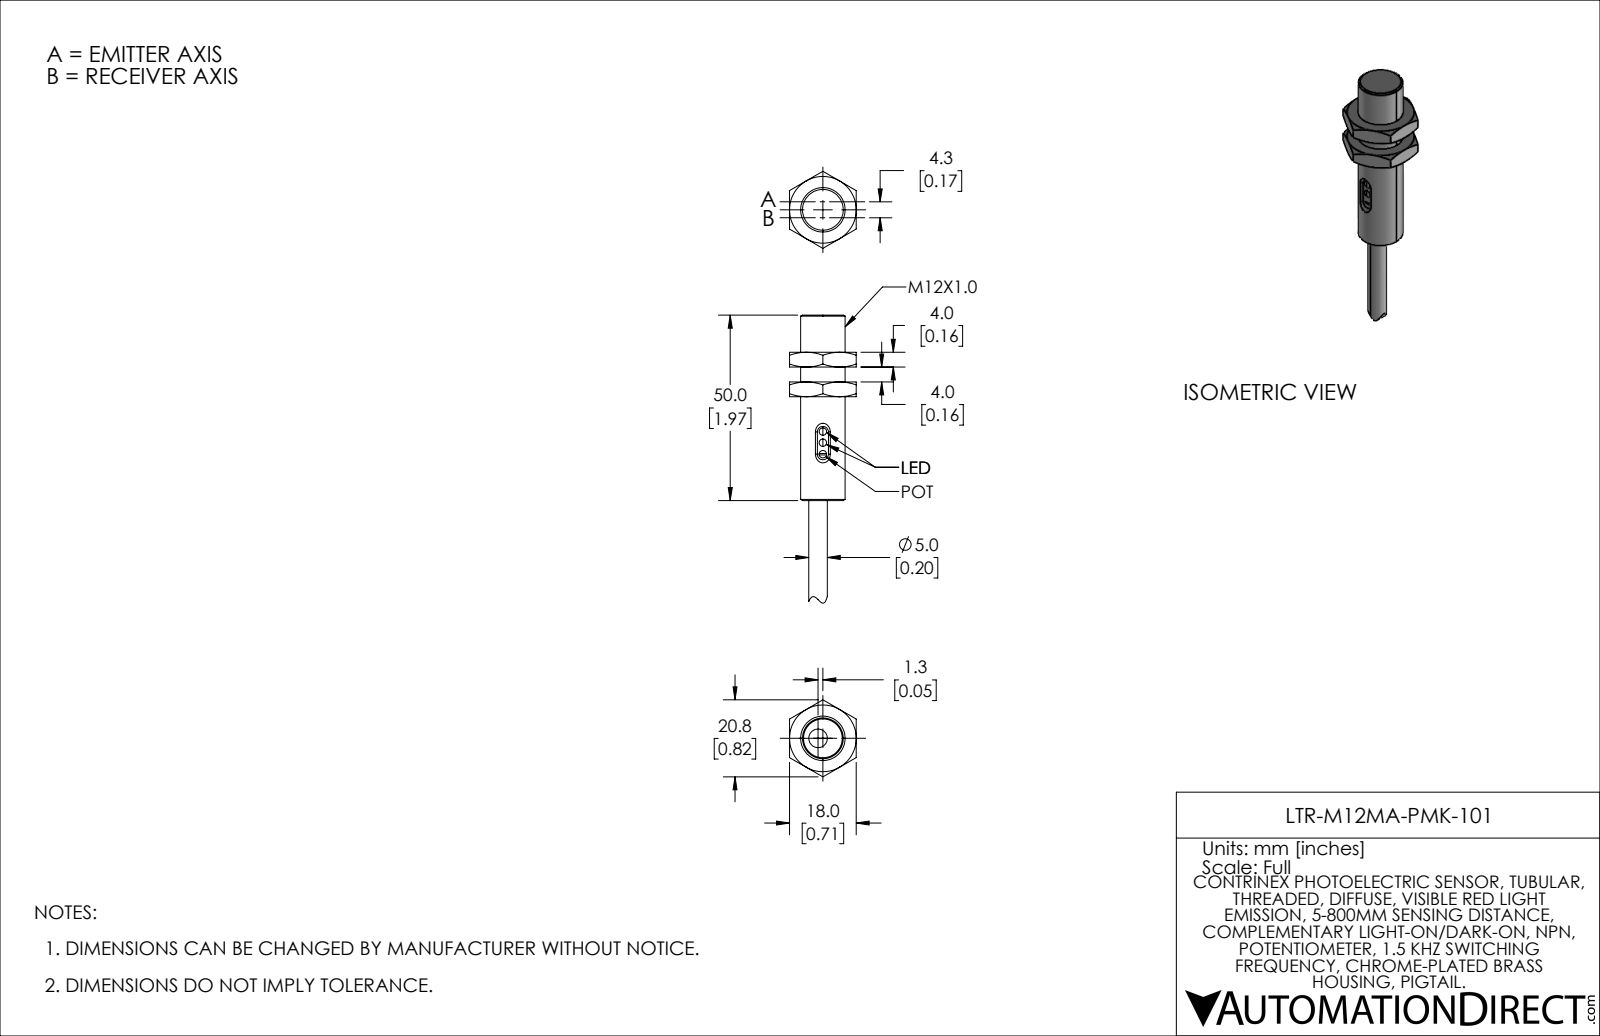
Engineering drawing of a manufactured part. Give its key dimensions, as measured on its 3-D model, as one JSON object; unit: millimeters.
{"part_name": "LTR-M12MA-PMK-101", "step_written_by": "SolidWorks 2021 (AUTOMOTIVE_DESIGN)", "units": "millimeters", "bodies": {"solids": 5, "faces": 104, "planar": 31, "cylindrical": 20, "other": 53}, "overall_size": [77.68, 20.79, 18], "volume_mm3": 8524, "surface_area_mm2": 4505, "round_holes": [[10.2, 1], [12, 1]], "round_bosses_or_shafts": [[5, 1]], "partial_cylinders_radius": [[1.5, 2], [1, 1]], "face_to_face_distances": [10, 18, 6, 16, 4, 40, 34, 30, 24, 20]}
